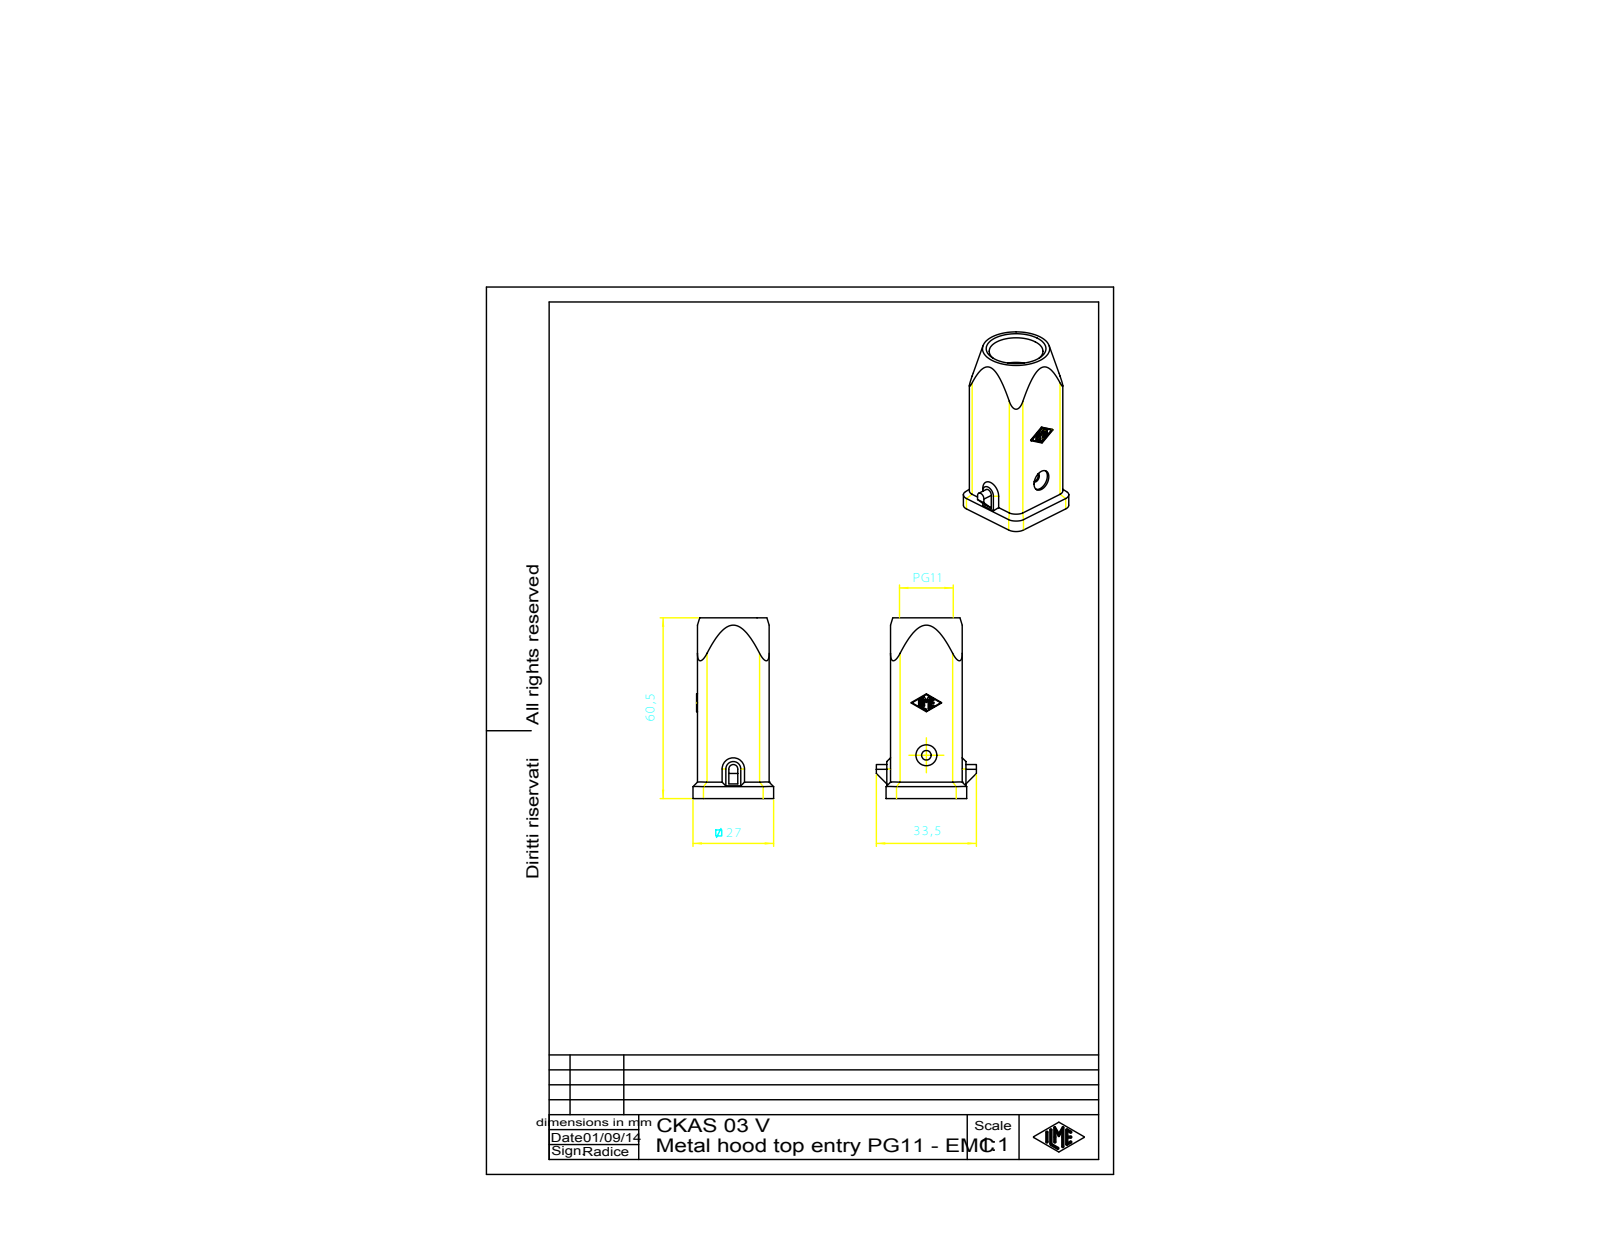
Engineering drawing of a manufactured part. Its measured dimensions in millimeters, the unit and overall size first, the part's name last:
Units: millimetres
Overall size (bounding box): 55 × 33.5 × 28
Round holes (diameter × count): ⌀3.3 ×1, ⌀15 ×1, ⌀17.26 ×1
Round bosses / shafts (diameter × count): ⌀6 ×1, ⌀3 ×1
Partial cylindrical surfaces — rounded edges, fillets, slot ends (radius × count): R0.25 ×14, R0.5 ×4, R1.5 ×4, R2 ×4, R3.5 ×4
Main face-to-face distances: 23, 1, 24, 22, 3, 1.5, 2, 25, 26, 0.5
Volume: 8 663 mm³ · Surface area: 10 532 mm²
Bodies: 1 solid, 126 faces (67 planar, 40 cylindrical, 19 other)
STEP written by: Autodesk Inventor 7 (AUTOMOTIVE_DESIGN)
